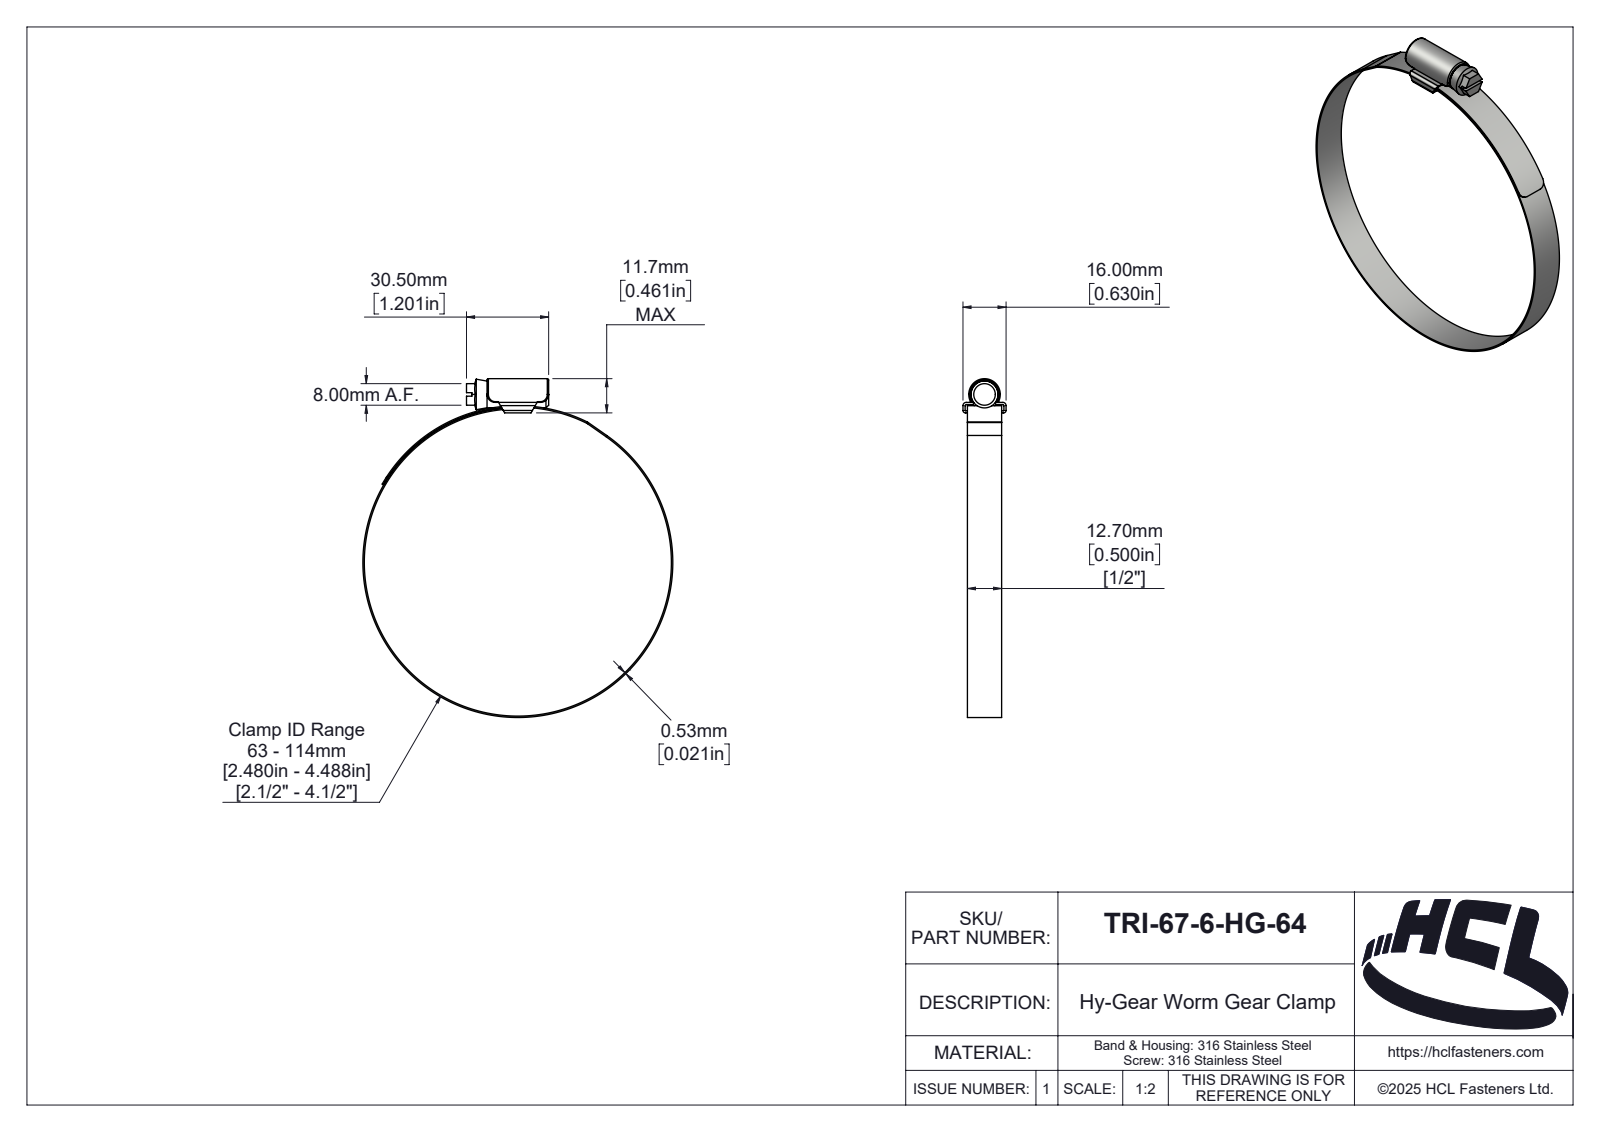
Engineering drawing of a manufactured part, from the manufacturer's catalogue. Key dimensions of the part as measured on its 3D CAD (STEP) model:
Part name (STEP PRODUCT): TRI-57-0-HG-64
STEP written by: SolidWorks 2025 (AUTOMOTIVE_DESIGN)
Units: millimetres
Bodies: 3 solids, 189 faces (39 planar, 89 cylindrical, 61 other)
Overall size (bounding box): 125.73 × 115.06 × 16
Volume: 5 823 mm³ · Surface area: 14 038 mm²
Round holes (diameter × count): ⌀114 ×1
Round bosses / shafts (diameter × count): ⌀115.06 ×1, ⌀10 ×1
Partial cylindrical surfaces — rounded edges, fillets, slot ends (radius × count): R0.5 ×6, R3 ×4, R0.1 ×2, R0.9 ×2, R1.2 ×2, R0.46 ×1, R1.89 ×1, R2 ×1
Main face-to-face distances: 0.8, 12.7, 3.1, 0.53, 2.3, 3.9, 30.5, 1.65, 14.35, 15.2
